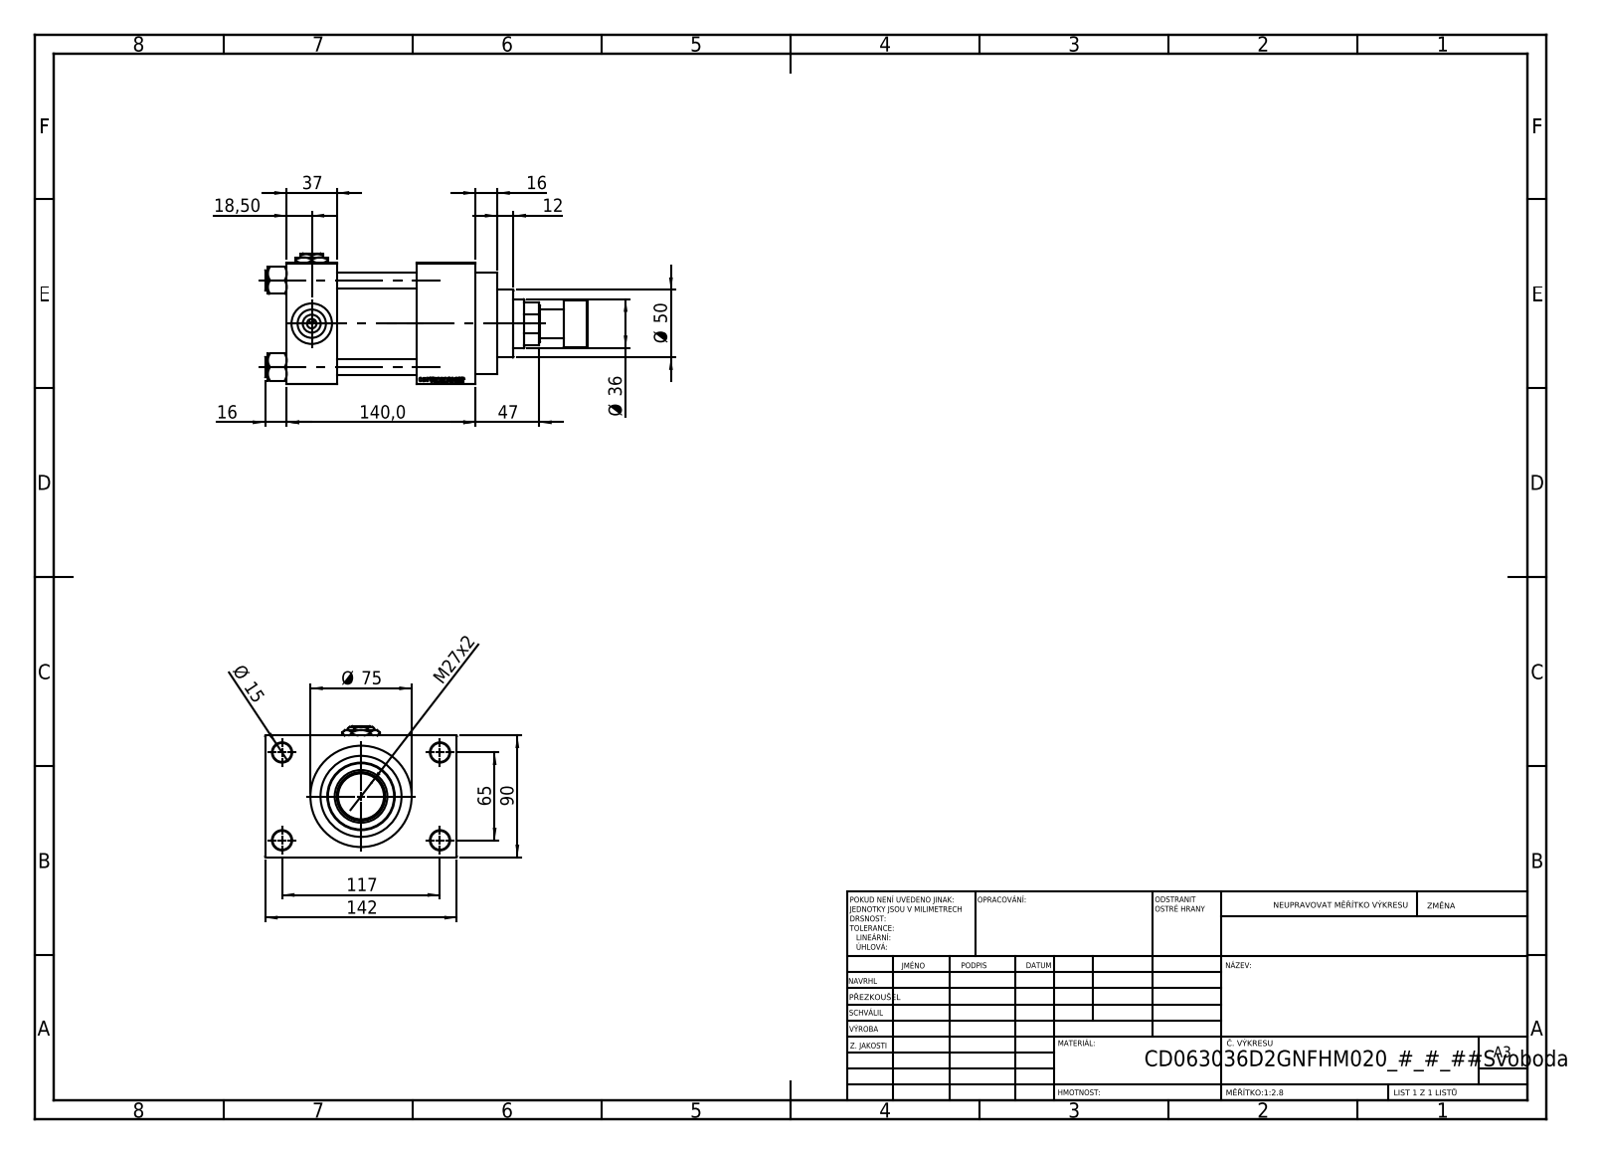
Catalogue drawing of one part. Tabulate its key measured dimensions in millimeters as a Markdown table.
| quantity | value |
| --- | --- |
| part name | V215CD_D_Body; V215CR_ROD_END_F; V215CD_D_TYCINKA; V215CD_VC_A (+3 more) |
| STEP written by | SolidWorks 2019 (CONFIG_CONTROL_DESIGN) |
| units | millimeters |
| bodies | 13 solids, 1170 faces (525 planar, 99 cylindrical, 546 other) |
| overall size | 239 × 142 × 97 |
| volume | 1 133 000 mm³ |
| surface area | 214 123 mm² |
| round holes (diameter × count) | 12 × 4, 14 × 4, 7 × 3, 20.96 × 3, 30 × 3, 25.5 × 1, 36 × 1, 39 × 1, 50 × 1, 60 × 1, 63 × 1 |
| round bosses / shafts (diameter × count) | 15 × 4, 75 × 1, 69 × 1, 35 × 1, 21 × 1 |
| main face-to-face distances | 90, 59, 37, 96, 140, 103, 44, 116, 26, 142 |
| hole center spacings | 26.35, 45.47, 64.3, 66.92, 69.81, 90.65, 111.34, 65 |
